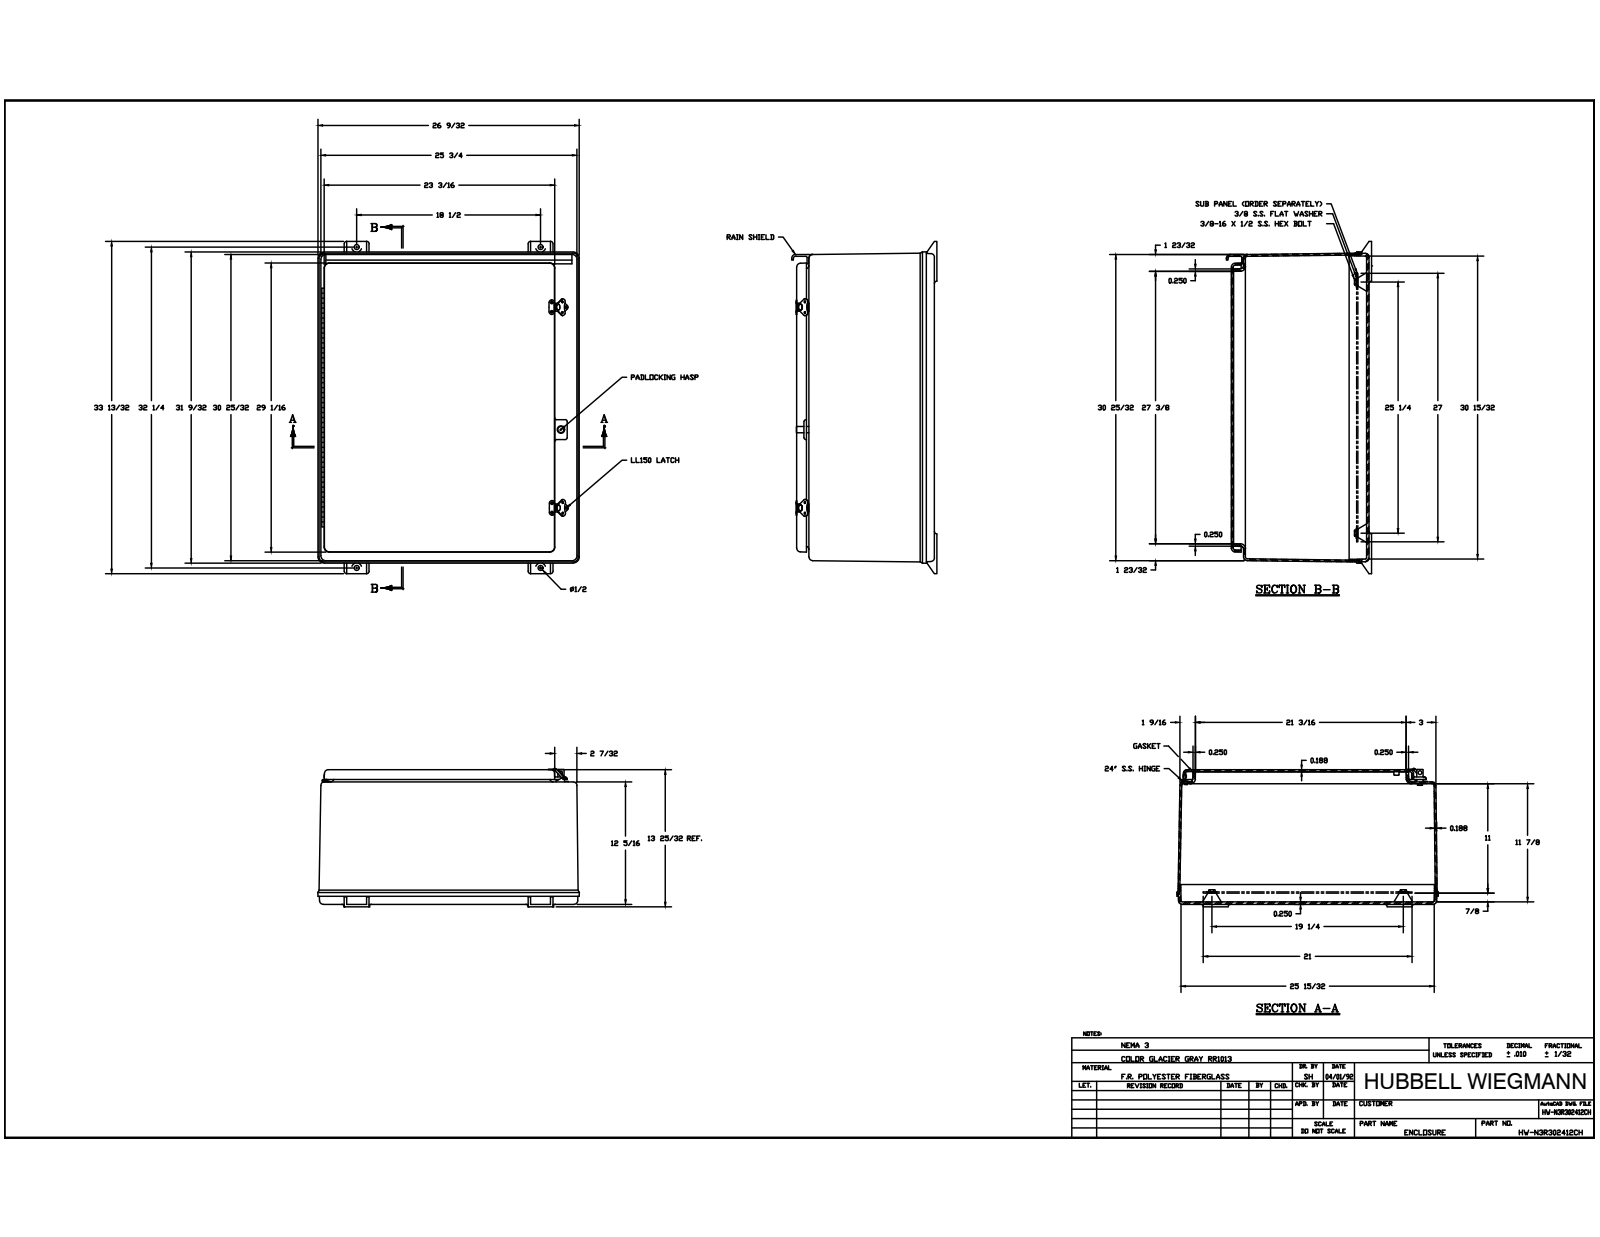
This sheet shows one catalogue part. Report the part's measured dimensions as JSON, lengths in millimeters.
{"part_name": "WPN302412SRT; WPN3024B; N3024RS; WPN302412RTPCVR (+8 more)", "step_written_by": "Autodesk Inventor 2014 (AUTOMOTIVE_DESIGN)", "units": "millimeters", "bodies": {"solids": 40, "faces": 1230, "planar": 490, "cylindrical": 486, "other": 254}, "overall_size": [848.52, 667.54, 363.54], "volume_mm3": 11360000, "surface_area_mm2": 4568000, "round_holes": [[3.3, 21], [1.59, 8], [2.54, 8], [5.11, 8], [3.5, 4], [4.76, 4], [14.3, 4], [1.65, 3], [7.14, 2], [12.95, 2], [12.96, 2], [3.17, 1]], "round_bosses_or_shafts": [[9.07, 8], [4.76, 8], [3.56, 8], [7.54, 3], [12.7, 2], [6.35, 1], [5.11, 1], [5.08, 1]], "partial_cylinders_radius": [[0.25, 60], [6.35, 24], [4.76, 22], [7.94, 14], [9.53, 12], [12.7, 12], [0.4, 8], [0.76, 8]], "face_to_face_distances": [4.76, 6.35, 4.77, 343.69, 337.34, 338.92, 332.57, 312.73, 30.96, 26.19], "hole_center_spacings": [190.5, 88.62, 393.7, 512.76, 620.87, 644.68, 729.16, 739.29]}
